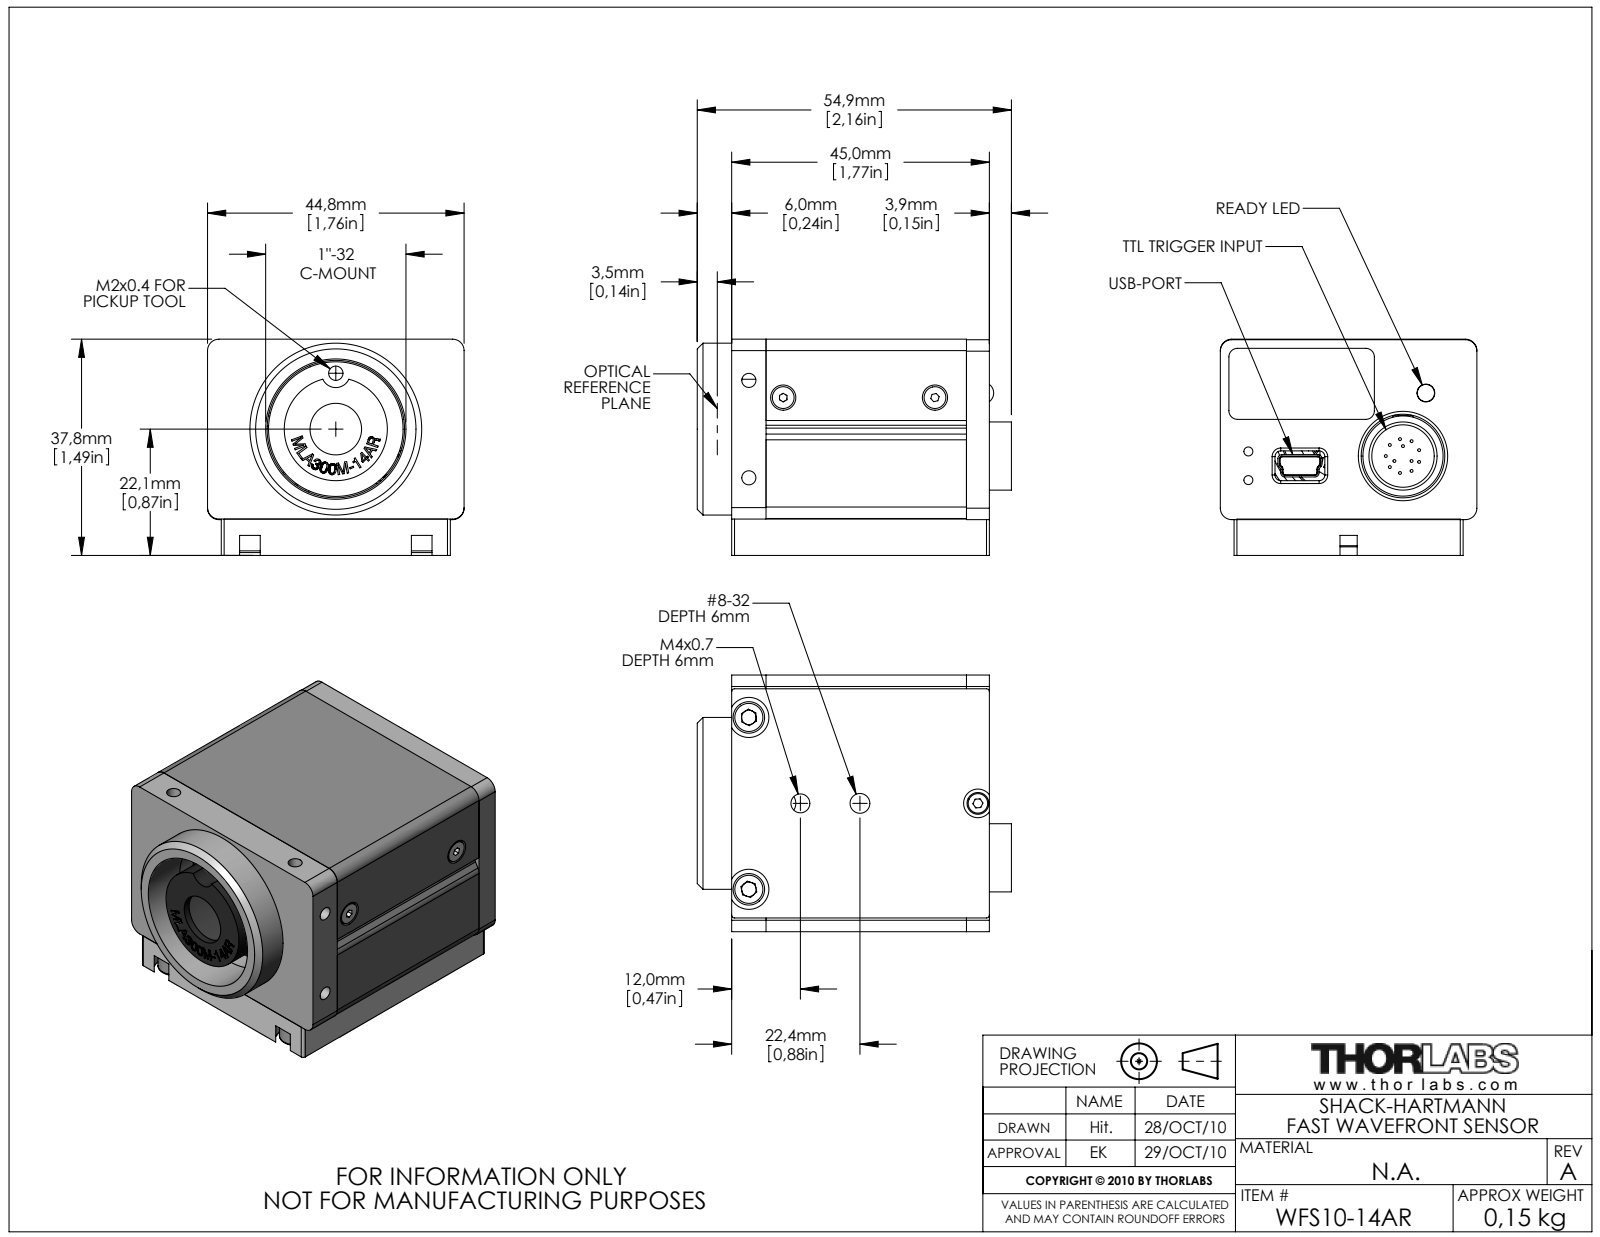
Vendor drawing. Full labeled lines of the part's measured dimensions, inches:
Part name (STEP PRODUCT): 21157-E0W
STEP written by: SolidWorks 2010 (CONFIG_CONTROL_DESIGN)
Units: inches
Bodies: 0 solids, 348 faces (182 planar, 125 cylindrical, 41 other)
Overall size (bounding box): 2.16 × 1.764 × 1.486
Round holes (diameter × count): ⌀0.097 ×3, ⌀0.097 ×2, ⌀0.276 ×2, ⌀0.062 ×1, ⌀0.062 ×1, ⌀0.122 ×1, ⌀0.13 ×1, ⌀0.136 ×1, ⌀0.197 ×1, ⌀0.354 ×1, ⌀0.429 ×1, ⌀0.575 ×1
Round bosses / shafts (diameter × count): ⌀0.02 ×12, ⌀0.15 ×3, ⌀0.217 ×2, ⌀1.181 ×1, ⌀0.709 ×1, ⌀0.469 ×1, ⌀0.118 ×1
Partial cylindrical surfaces — rounded edges, fillets, slot ends (radius × count): R0.079 ×12, R0.012 ×8, R0.039 ×6, R0.02 ×4, R0.028 ×4, R0.059 ×4, R0.098 ×1
Main face-to-face distances: 1.486, 1.232, 0.254, 1.764, 1.772, 0.094, 1.669, 0.039, 1.724, 0.055
Hole centre spacings: 0.689, 0.965, 1.682, 0.197, 0.409, 0.417, 0.461, 0.587
